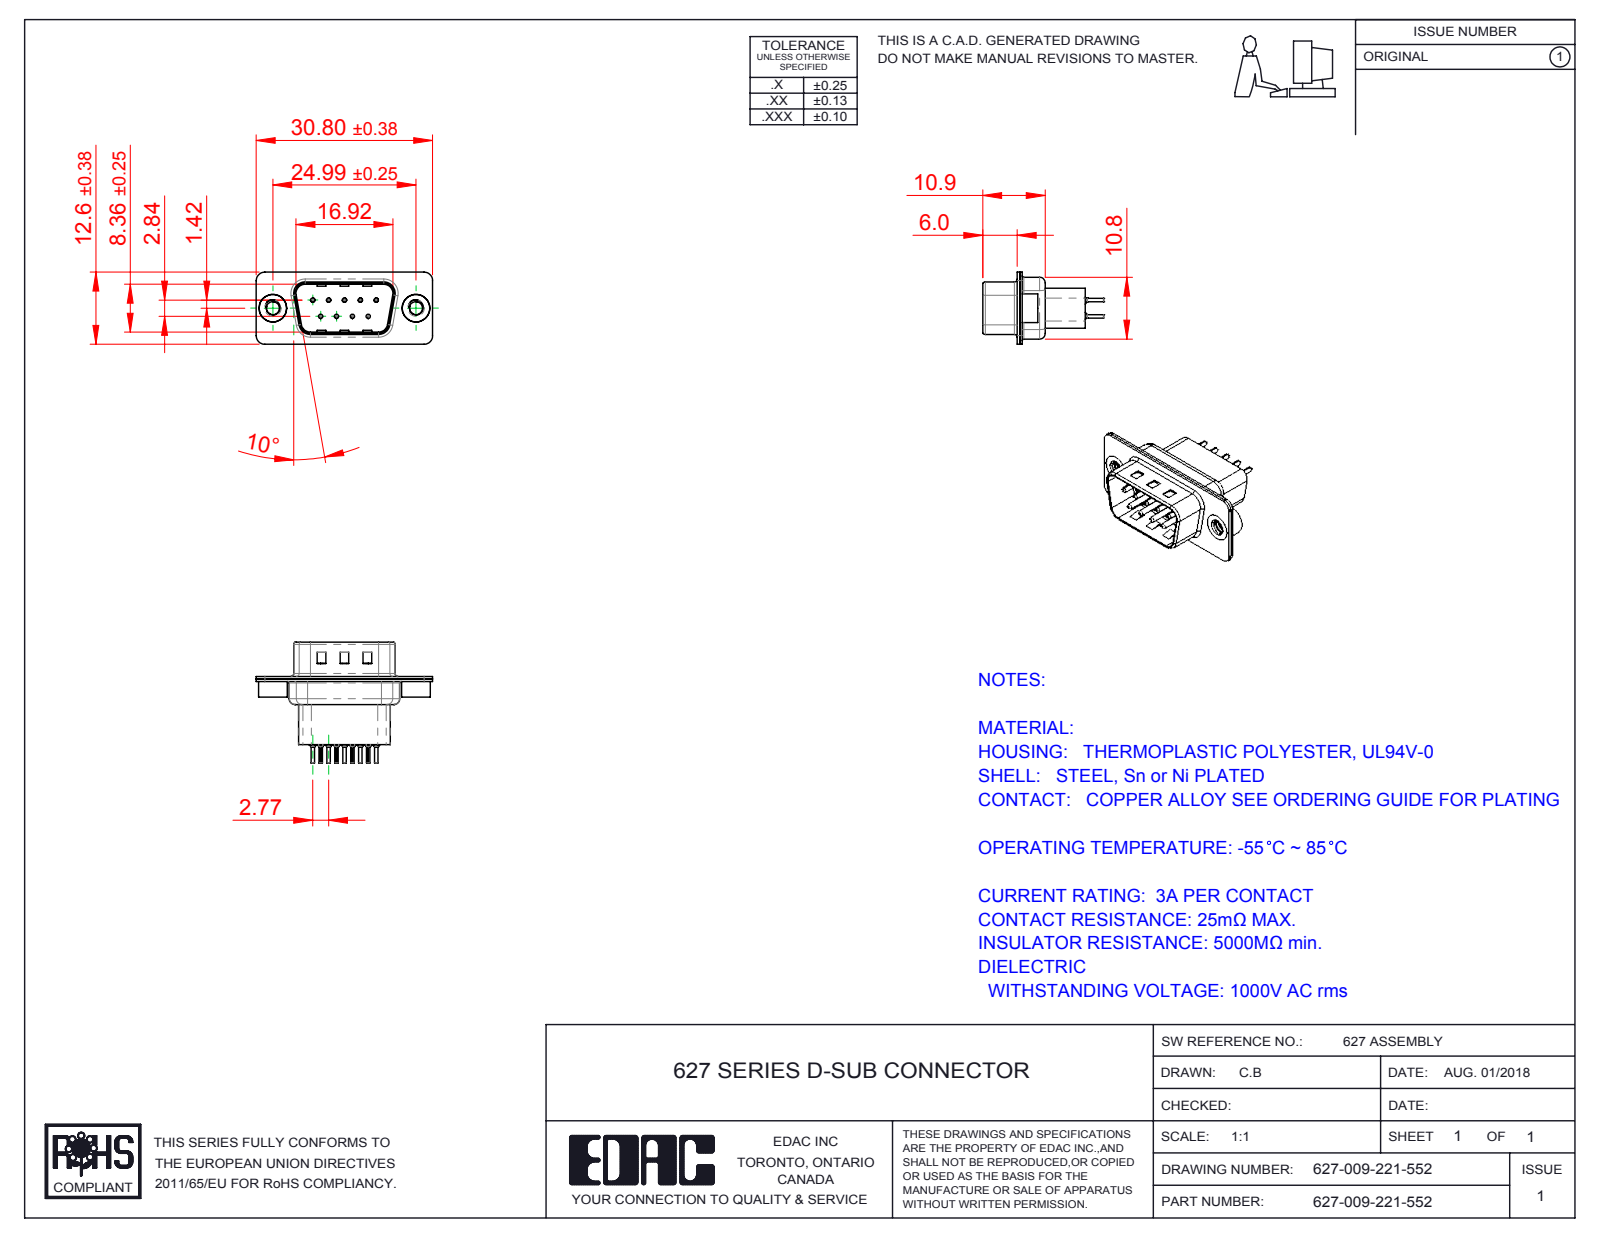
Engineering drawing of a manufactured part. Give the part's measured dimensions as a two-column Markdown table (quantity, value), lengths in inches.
| quantity | value |
| --- | --- |
| part name | 627 4-40 Threaded Rivet; 627 Contact Row 1_21H; 627 Shell Front_09 Contacts; 627 Shell Rear_09 Contacts (+3 more) |
| STEP written by | SolidWorks 2016 (CONFIG_CONTROL_DESIGN) |
| units | inches |
| bodies | 14 solids, 1186 faces (323 planar, 462 cylindrical, 401 other) |
| overall size | 1.213 × 0.831 × 0.496 |
| volume | 0.111 in³ |
| surface area | 7.412 in² |
| round holes (diameter × count) | 0.008 × 9, 0.014 × 9, 0.043 × 9, 0.063 × 9, 0.089 × 2, 0.157 × 2, 0.189 × 2 |
| round bosses / shafts (diameter × count) | 0.079 × 9, 0.059 × 9, 0.03 × 9, 0.024 × 9, 0.197 × 2, 0.193 × 2 |
| partial cylindrical surfaces (radius × count) | 0.004 × 18, 0.059 × 18, 0.079 × 12, 0.02 × 8, 0.063 × 8, 0.01 × 4, 0.024 × 4, 0.026 × 4 |
| main face-to-face distances | 0.018, 0.016, 0.035, 0.032, 0.377, 0.055, 0.059, 0.027, 0.302, 0.043 |
| hole center spacings | 0.124, 0.109, 0.218, 0.198, 0.198, 0.327, 0.294, 0.295 |
